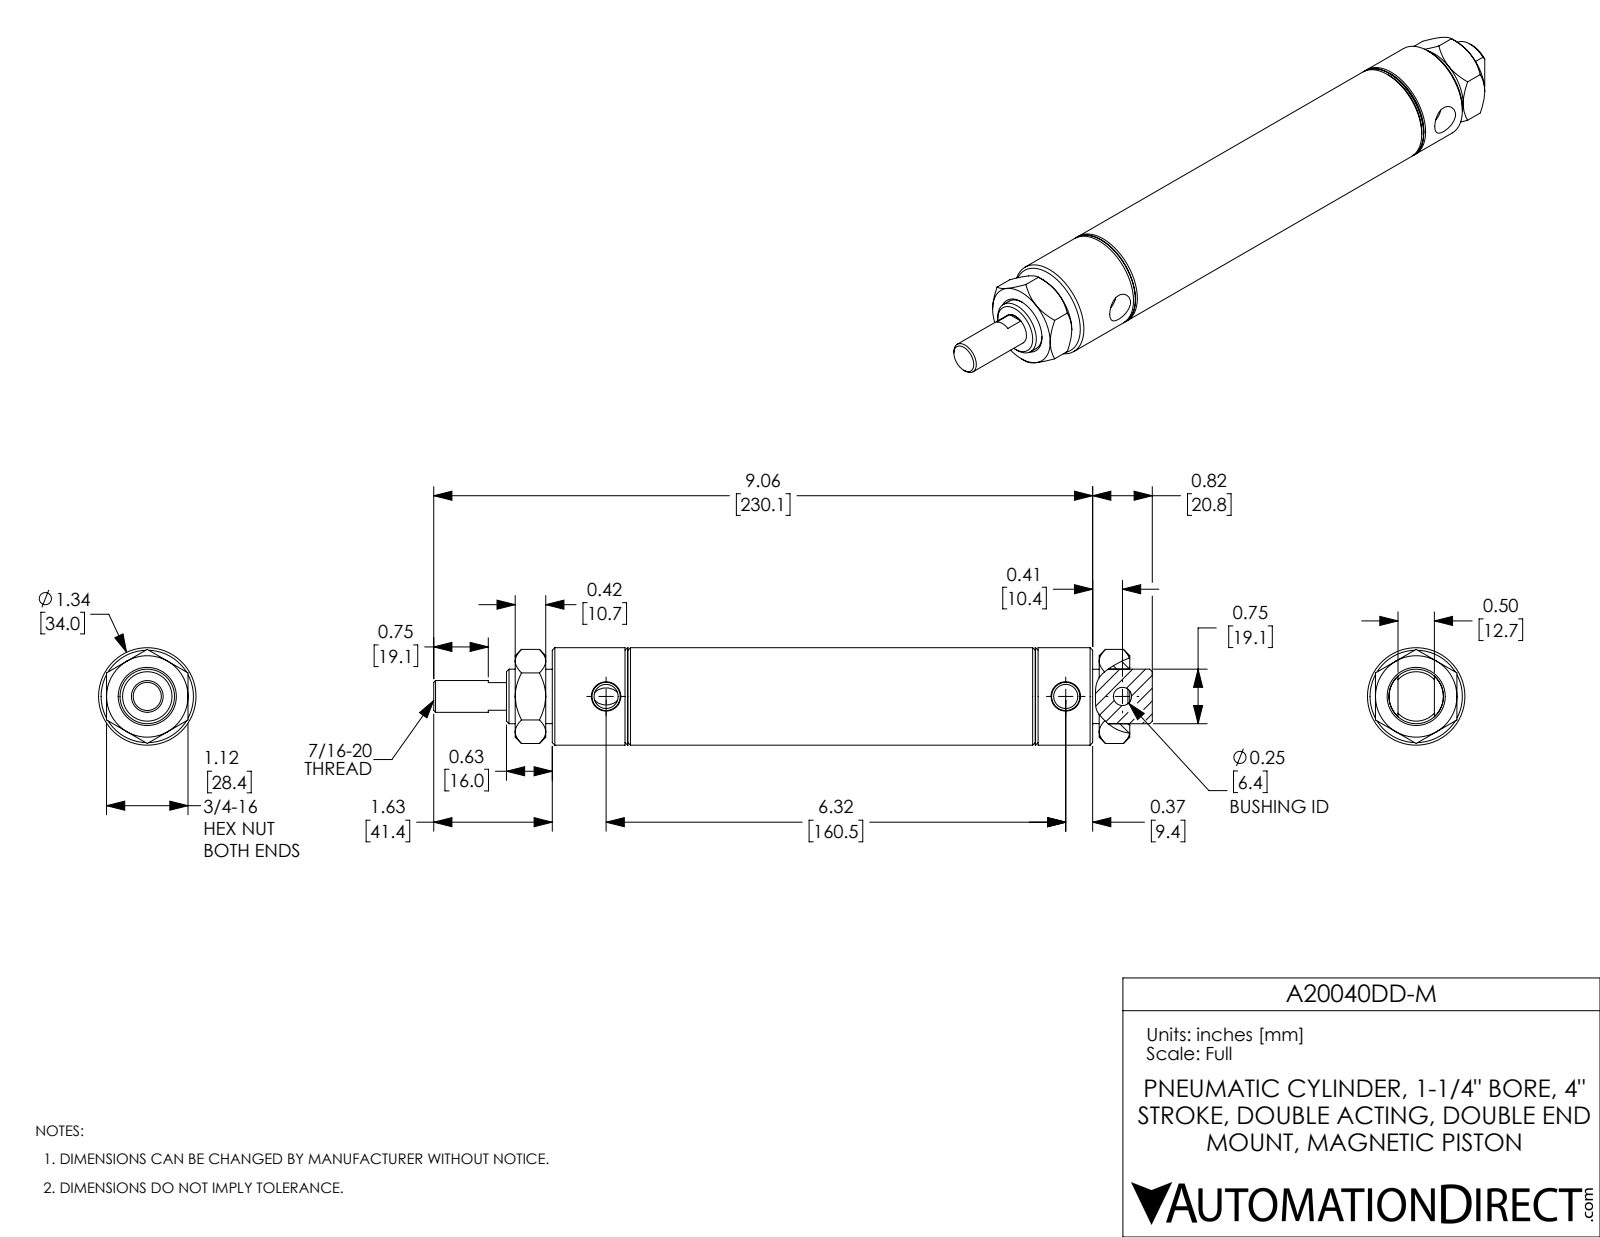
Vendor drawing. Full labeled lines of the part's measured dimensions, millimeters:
Part name (STEP PRODUCT): A20040DD-M-Rod; A20040DD-M-MainBody; A20040DD-M; A20040DD-M_Mounting Nut_D-3556
STEP written by: SolidWorks 2017 (AUTOMOTIVE_DESIGN)
Units: millimetres
Bodies: 4 solids, 138 faces (44 planar, 36 cylindrical, 58 other)
Overall size (bounding box): 251 × 34 × 34
Volume: 119 200 mm³ · Surface area: 53 800 mm²
Round holes (diameter × count): ⌀8.4 ×2, ⌀6.4 ×1, ⌀11.1 ×1, ⌀19.1 ×1, ⌀31.8 ×1
Round bosses / shafts (diameter × count): ⌀34 ×1, ⌀19 ×1
Main face-to-face distances: 37.2, 151.5, 12.7, 28.4, 114.3, 101.6, 7.9, 10.7, 204, 49.9
Hole centre spacings: 19.8, 160.5, 180.3
